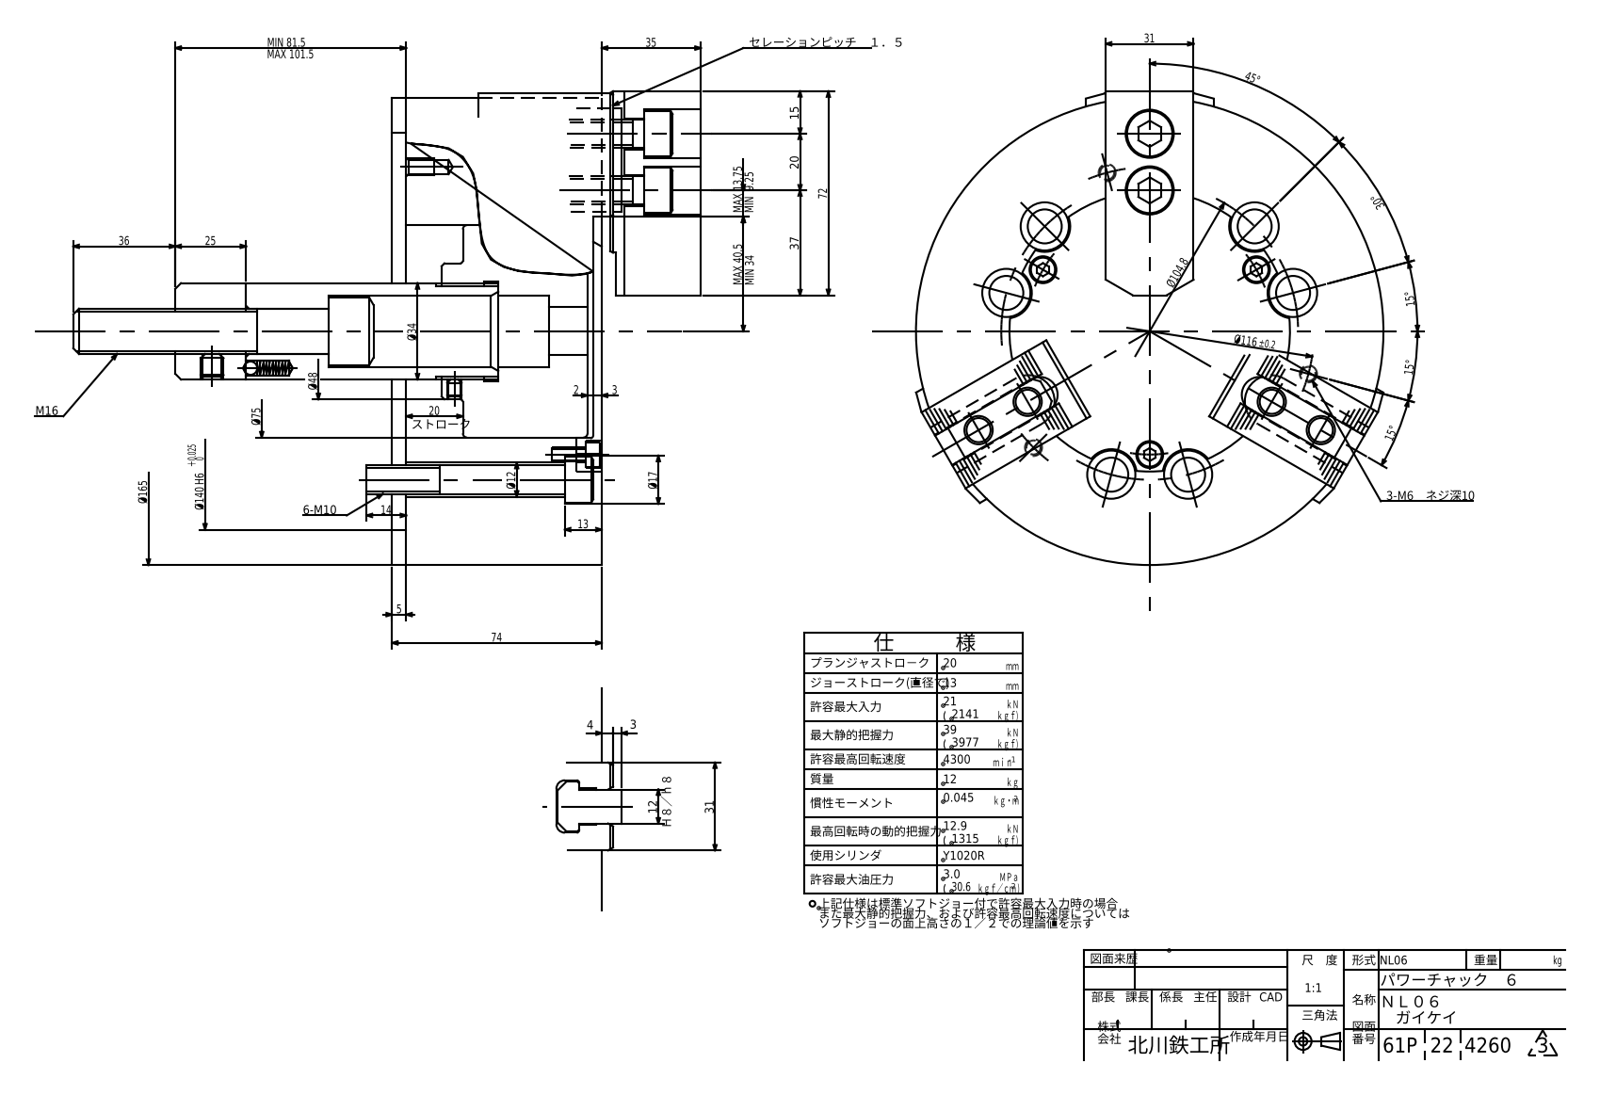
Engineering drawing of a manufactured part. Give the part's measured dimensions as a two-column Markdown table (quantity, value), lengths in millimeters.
| quantity | value |
| --- | --- |
| part name | 61P211225_NL06_ASSY |
| STEP written by | ST-DEVELOPER v16.7 (AUTOMOTIVE_DESIGN) |
| units | millimeters |
| bodies | 27 solids, 2189 faces (1929 planar, 153 cylindrical, 107 other) |
| overall size | 221.7 × 171.75 × 169.49 |
| volume | 1 553 000 mm³ |
| surface area | 318 279 mm² |
| round holes (diameter × count) | 5 × 13, 17 × 13, 12 × 9, 6 × 6, 10 × 6, 11 × 6, 4.2 × 3, 5.5 × 3, 9.5 × 3, 13.5 × 3, 15 × 3, 20 × 3 |
| round bosses / shafts (diameter × count) | 16 × 6, 18 × 3, 8.5 × 3, 165 × 1, 75 × 1, 48 × 1, 32 × 1, 24 × 1 |
| partial cylindrical surfaces (radius × count) | 3.6 × 6, 9 × 6, 6.3 × 3, 9.25 × 3, 37.75 × 1, 49.5 × 1 |
| main face-to-face distances | 31, 69, 5, 14, 9.5, 21.5, 0.5, 7, 38, 4 |
| hole center spacings | 15.31, 51.59, 76.26, 90.74, 43.5, 40.85, 42.08, 49.75 |
